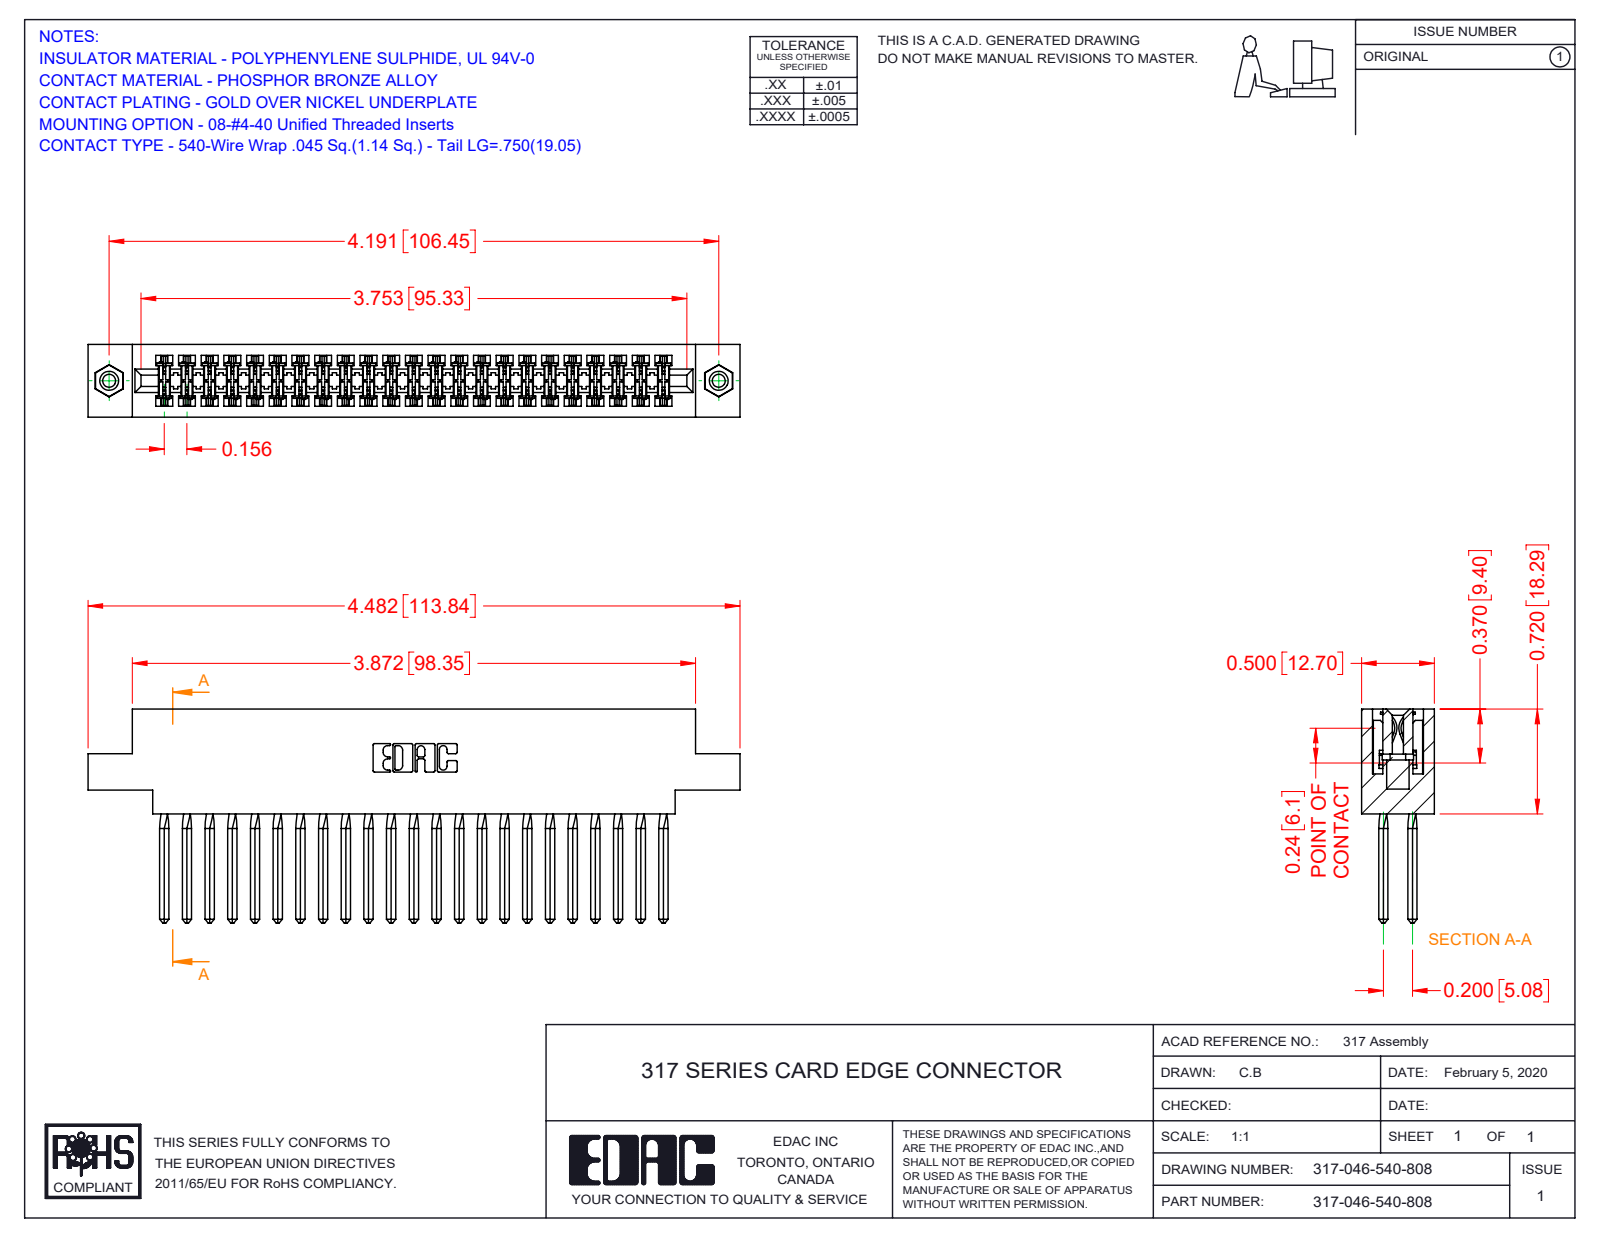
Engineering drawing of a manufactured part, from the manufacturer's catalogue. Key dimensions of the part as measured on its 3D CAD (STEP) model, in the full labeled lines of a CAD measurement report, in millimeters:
Part name (STEP PRODUCT): 345-250-001_345-250-003-102; 317-290-001_540; 317 Part_.156 Dia - TI; 317-046-540-808
STEP written by: SolidWorks 2016 (CONFIG_CONTROL_DESIGN)
Units: millimetres
Bodies: 49 solids, 4256 faces (3448 planar, 608 cylindrical, 200 other)
Overall size (bounding box): 113.8 × 37.3 × 12.7
Volume: 18 450 mm³ · Surface area: 26 830 mm²
Round holes (diameter × count): ⌀2.3 ×2, ⌀3.2 ×2, ⌀4 ×2
Round bosses / shafts (diameter × count): ⌀3.9 ×2
Partial cylindrical surfaces — rounded edges, fillets, slot ends (radius × count): R0.4 ×92, R0.3 ×22, R0.2 ×6, R0.8 ×6, R0.7 ×3, R2.4 ×2, R2.5 ×2, R2.8 ×2
Main face-to-face distances: 12.7, 1.9, 10.8, 8.9, 2.8, 5, 2.4, 18.3, 5.1, 2.9
Hole centre spacings: 106.5
